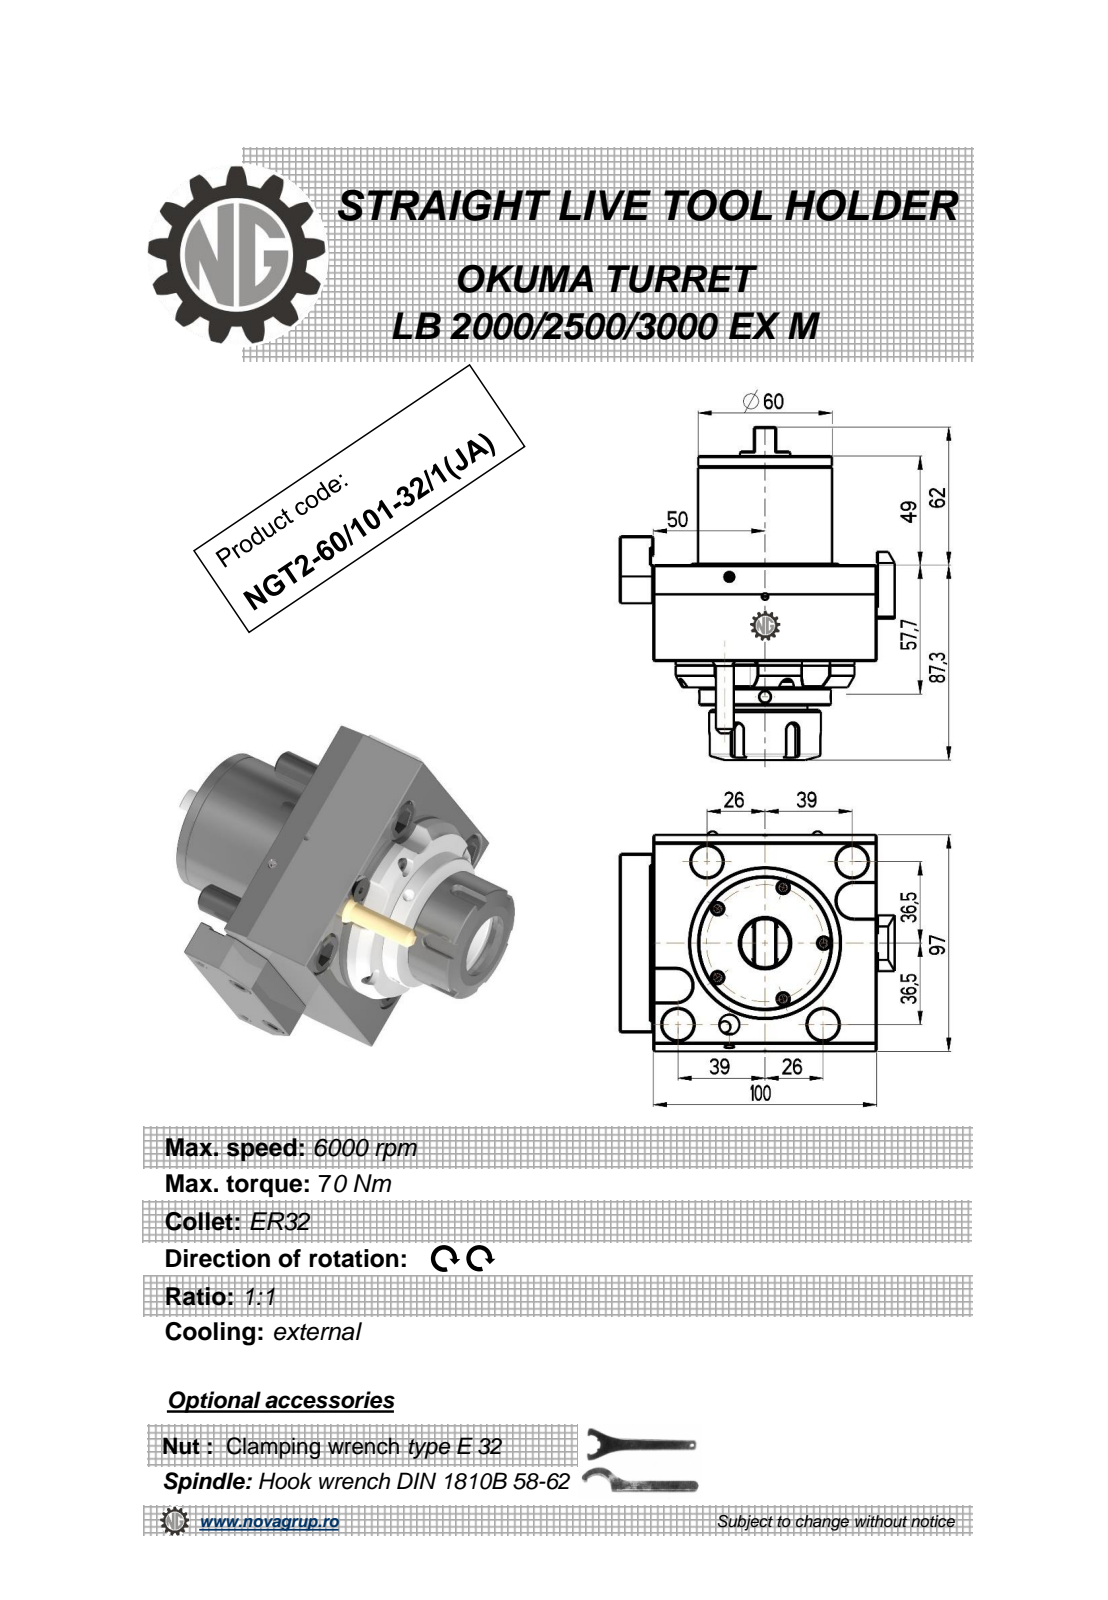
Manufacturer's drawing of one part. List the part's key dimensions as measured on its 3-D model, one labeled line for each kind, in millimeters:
Part name (STEP PRODUCT): NGT2_60_101_32_1_JA
STEP written by: PRO/ENGINEER BY PARAMETRIC TECHNOLOGY CORPORATION, 2010280 (CONFIG_CONTROL_DESIGN)
Units: millimetres
Bodies: 1 solid, 326 faces (144 planar, 81 cylindrical, 101 other)
Overall size (bounding box): 149.3 × 123 × 97
Volume: 716 701 mm³ · Surface area: 69 797 mm²
Round holes (diameter × count): ⌀5 ×6, ⌀3 ×1, ⌀9 ×1, ⌀27 ×1
Round bosses / shafts (diameter × count): ⌀12 ×4, ⌀6 ×2, ⌀80 ×1, ⌀60 ×1, ⌀59 ×1, ⌀50 ×1, ⌀47 ×1, ⌀41 ×1
Partial cylindrical surfaces — rounded edges, fillets, slot ends (radius × count): R0.31 ×10, R3 ×5, R0.8 ×2, R6 ×2, R9.5 ×2, R7.5 ×1, R8 ×1
Main face-to-face distances: 43, 100, 97, 49, 54.7, 11.7, 92, 103.7, 15, 115
Hole centre spacings: 39.41, 73.3, 2.24, 39.85, 41.6, 42.95, 64
